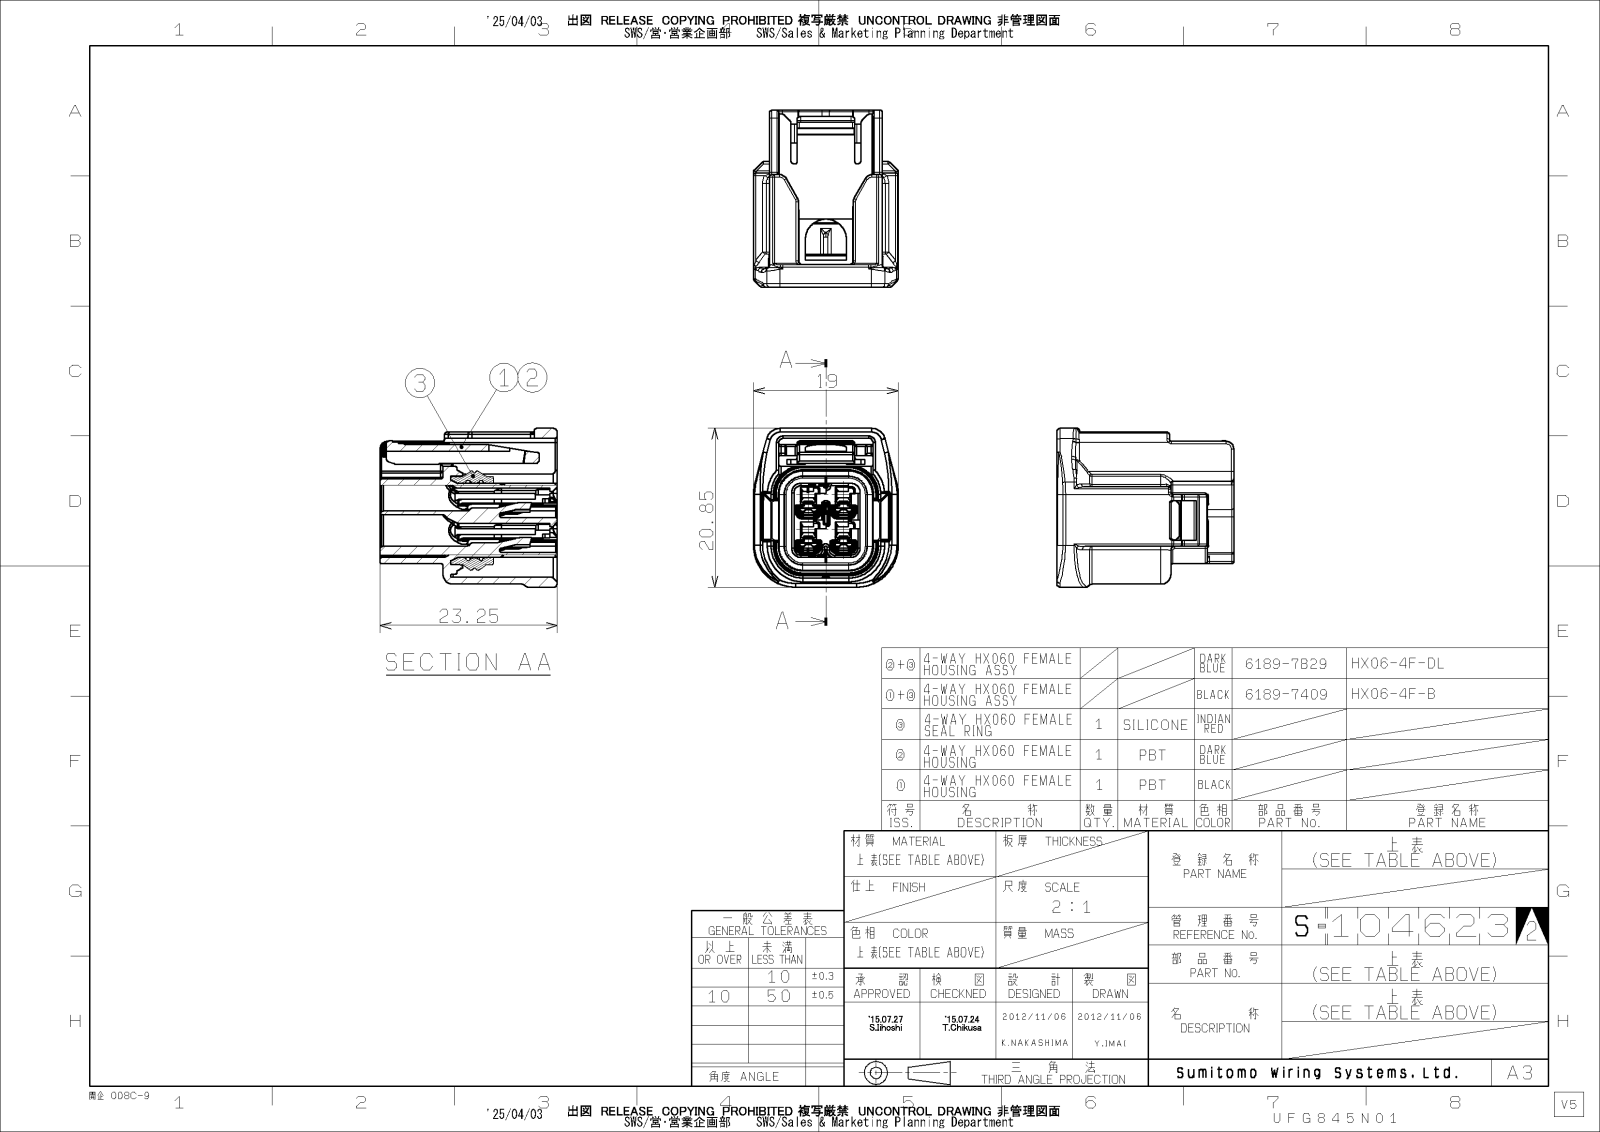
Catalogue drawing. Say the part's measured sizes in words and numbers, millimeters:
The part is named "6189-7409". Its 3-D file was written by "CATIA V5 STEP AP214 v2 (AUTOMOTIVE_DESIGN)". It is 1 solid with 250 faces: 188 planar, 56 cylindrical and 6 other. Overall it measures 23.25 by 20.82 by 19 millimeters. Its volume is 3 823 cubic millimeters and its surface area 4 224 square millimeters. Round holes: 4 of diameter 4.1. Partial cylindrical surfaces (rounded edges, fillets, slot ends): 7 of radius 1, 4 of radius 1.25, 4 of radius 1.5, 4 of radius 1.8, 4 of radius 2.95, 4 of radius 3.7, 4 of radius 4.2, 4 of radius 5. The main face-to-face distances are 15.7, 1.2, 2.1, 14, 11.9, 3.3, 5, 10.7, 1.7, 1. The hole center spacings are 4.59, 4.6, 6.5.
